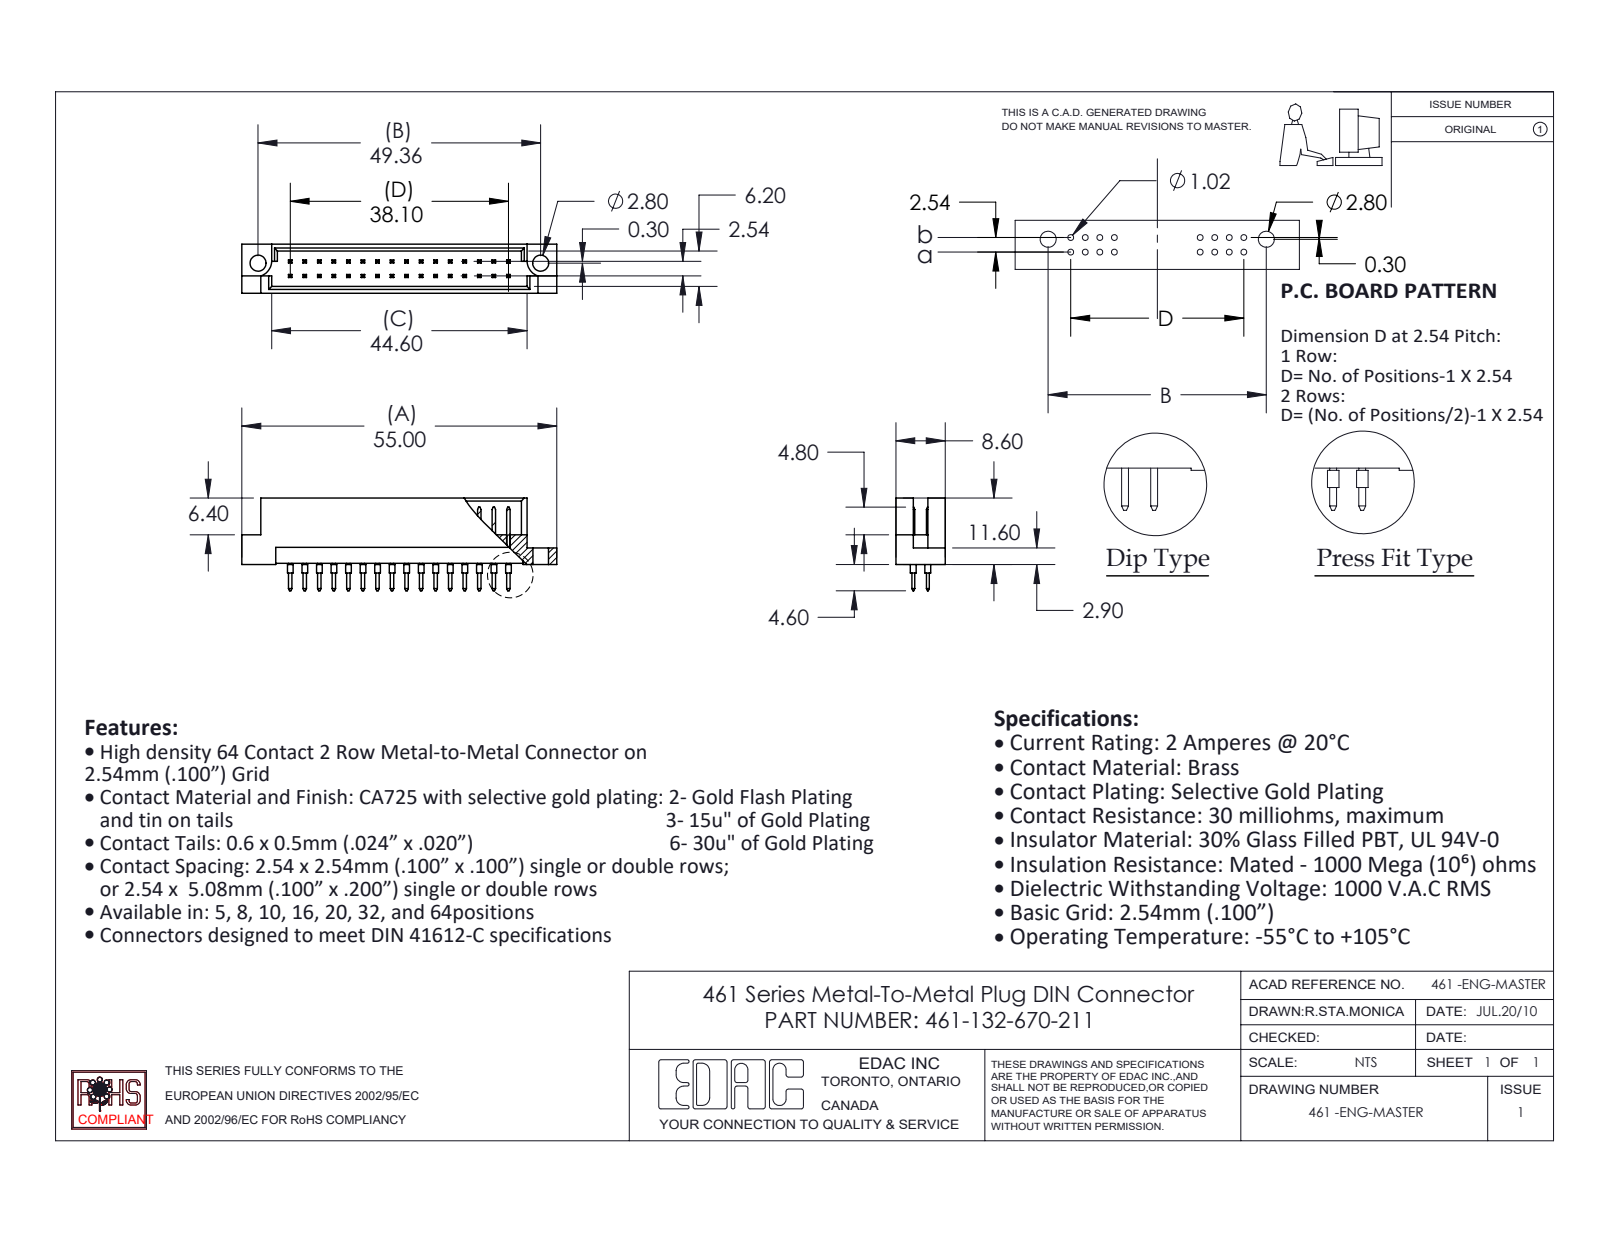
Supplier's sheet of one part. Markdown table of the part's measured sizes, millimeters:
| quantity | value |
| --- | --- |
| part name | 461 Part_32; 461-132-670-211; 461-290_70 |
| STEP written by | SolidWorks 2020 (CONFIG_CONTROL_DESIGN) |
| units | millimeters |
| bodies | 33 solids, 880 faces (810 planar, 70 cylindrical, 0 other) |
| overall size | 55 × 16.2 × 8.6 |
| volume | 2 814 mm³ |
| surface area | 4 339 mm² |
| round holes (diameter × count) | 2.8 × 2 |
| round bosses / shafts (diameter × count) | 1 × 32 |
| partial cylindrical surfaces (radius × count) | 2.8 × 2 |
| main face-to-face distances | 1.2, 7.4, 2.54, 8.6, 6.2, 1.58, 2.78, 5.82, 4.62, 3.28 |
| hole center spacings | 49.36 |
